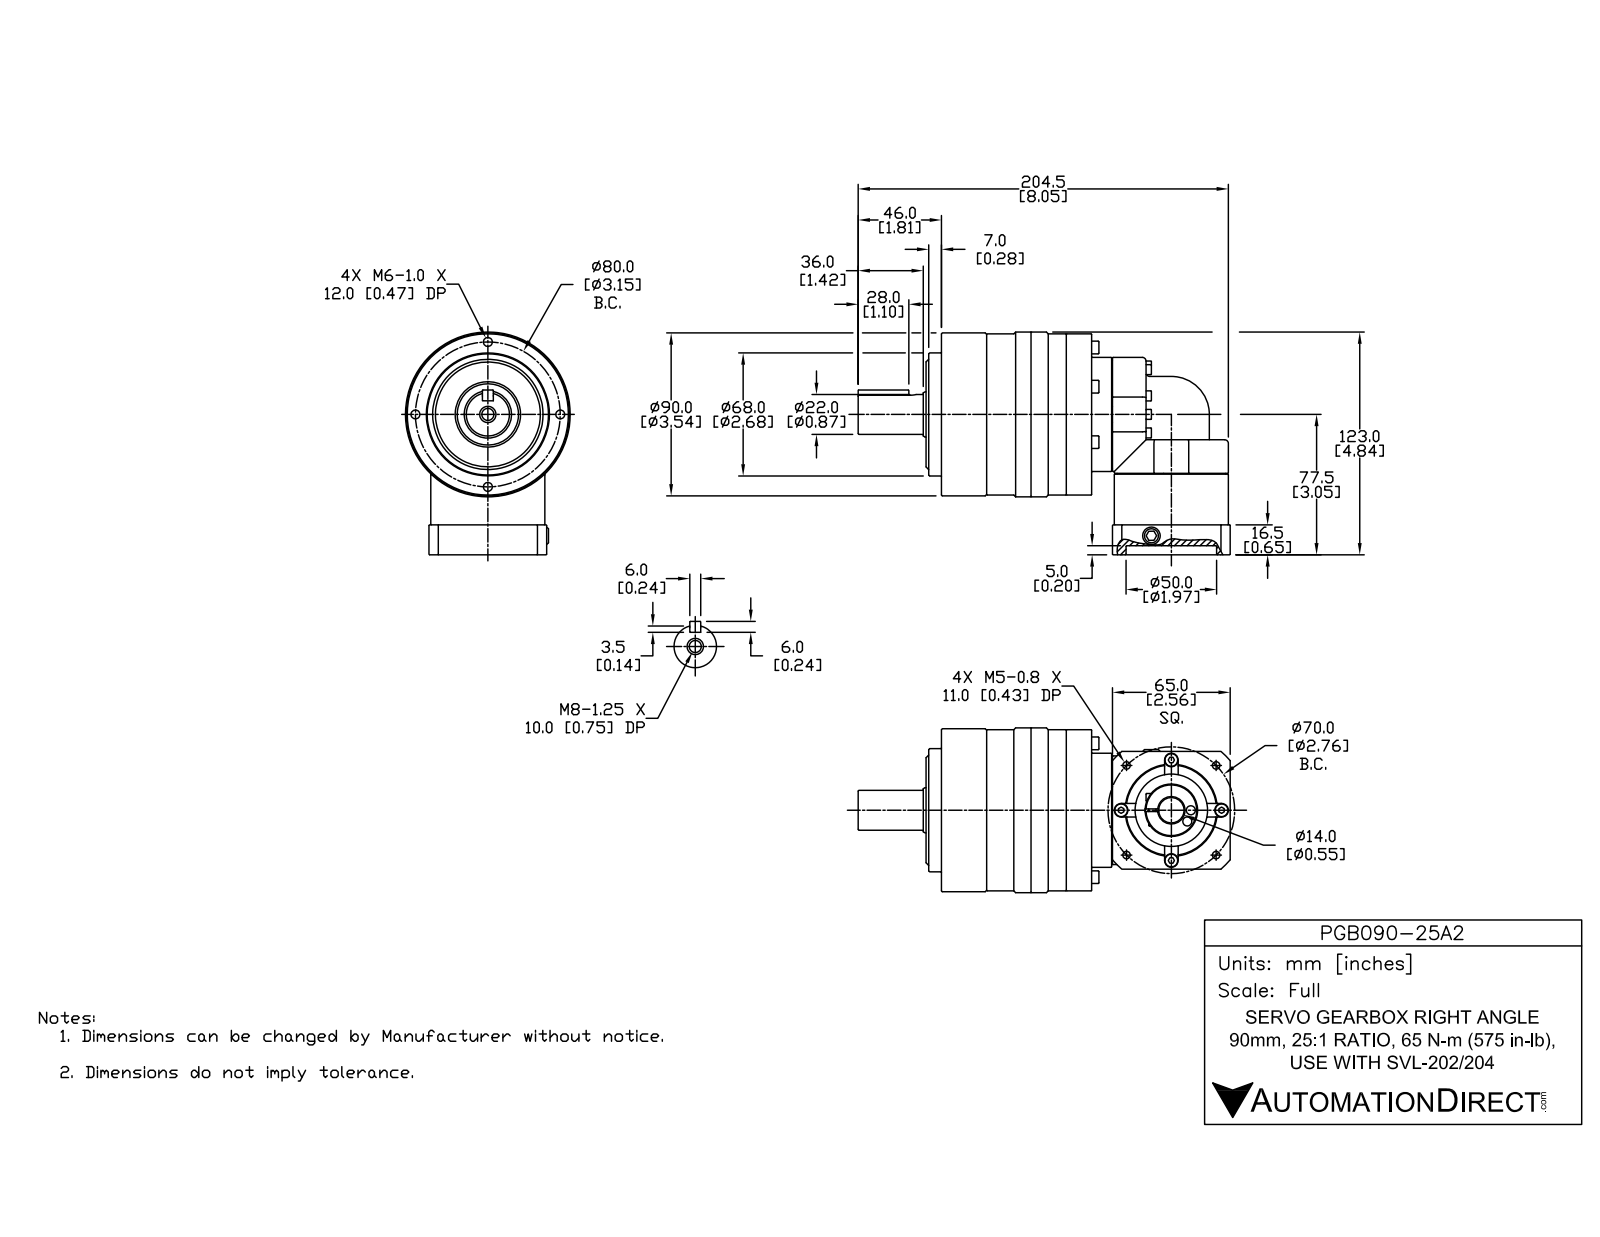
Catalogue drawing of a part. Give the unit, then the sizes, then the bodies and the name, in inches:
Units: inches
Overall size (bounding box): 8.091 × 4.843 × 3.583
Round holes (diameter × count): ⌀0.177 ×7, ⌀0.163 ×4, ⌀0.194 ×4, ⌀0.295 ×4, ⌀0.197 ×2, ⌀0.262 ×1, ⌀0.315 ×1, ⌀0.551 ×1, ⌀1.142 ×1, ⌀1.575 ×1, ⌀1.969 ×1
Round bosses / shafts (diameter × count): ⌀0.276 ×11, ⌀0.217 ×9, ⌀0.157 ×7, ⌀2.48 ×2, ⌀2.362 ×2, ⌀3.583 ×1, ⌀3.543 ×1, ⌀3.504 ×1
Partial cylindrical surfaces — rounded edges, fillets, slot ends (radius × count): R0.079 ×6, R0.827 ×2, R0.064 ×1, R0.118 ×1, R0.157 ×1, R1.673 ×1
Main face-to-face distances: 0.453, 3.268, 0.335, 3.602, 2.559, 0.65, 0.098, 2.461, 0.059, 3.72
Hole centre spacings: 0.981, 2.285, 0.615, 1.575, 1.75, 2.619, 3.089, 1.206
Volume: 53.54 in³ · Surface area: 120.6 in²
Bodies: 1 solid, 642 faces (271 planar, 165 cylindrical, 206 other)
Part name (STEP PRODUCT): PGB090-25A2
STEP written by: SolidWorks 2014 (AUTOMOTIVE_DESIGN)
